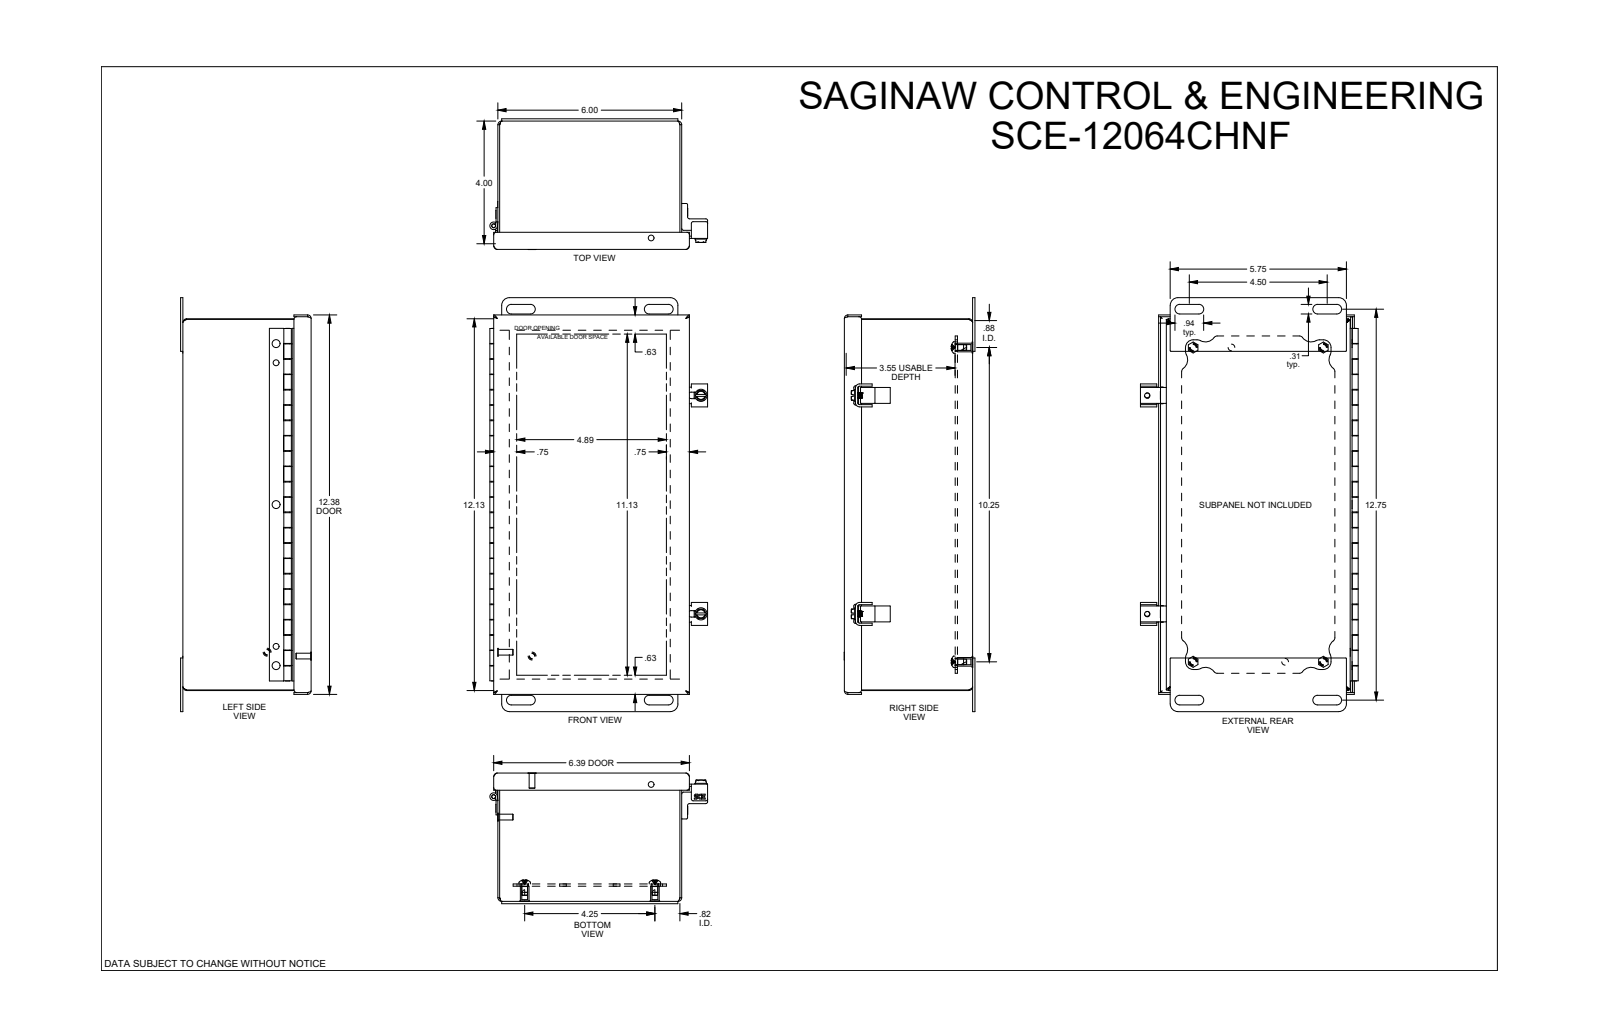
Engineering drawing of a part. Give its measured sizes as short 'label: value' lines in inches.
name: SCE-12064CHNF
written by: SolidWorks 2019 (AUTOMOTIVE_DESIGN)
unit: in
bodies: 37 solids, 1263 faces (563 planar, 353 cylindrical, 347 other)
size: 13.5 × 7.104 × 4.265
volume: 29.03 in³; area: 903.3 in²
holes: 9× ⌀0.19, 7× ⌀0.193, 4× ⌀0.25, 4× ⌀0.281, 2× ⌀0.156, 2× ⌀0.218, 2× ⌀0.266, 1× ⌀0.126, 1× ⌀0.187
bosses: 11× ⌀0.188, 7× ⌀0.256, 4× ⌀0.373, 4× ⌀0.28, 2× ⌀0.396, 2× ⌀0.188, 1× ⌀0.246, 1× ⌀0.123
rounds: 76× R0.01, 33× R0.06, 16× R0.25, 8× R0.05, 8× R0.125, 8× R0.156, 8× R0.344, 6× R0.027
face distances: 0.06, 4.125, 5.94, 4.185, 4.065, 0.075, 0.51, 0.435, 0.57, 3.555
hole spacings: 5.959, 10.249, 11.096, 1.065, 1.25, 2.165, 2.166, 3
